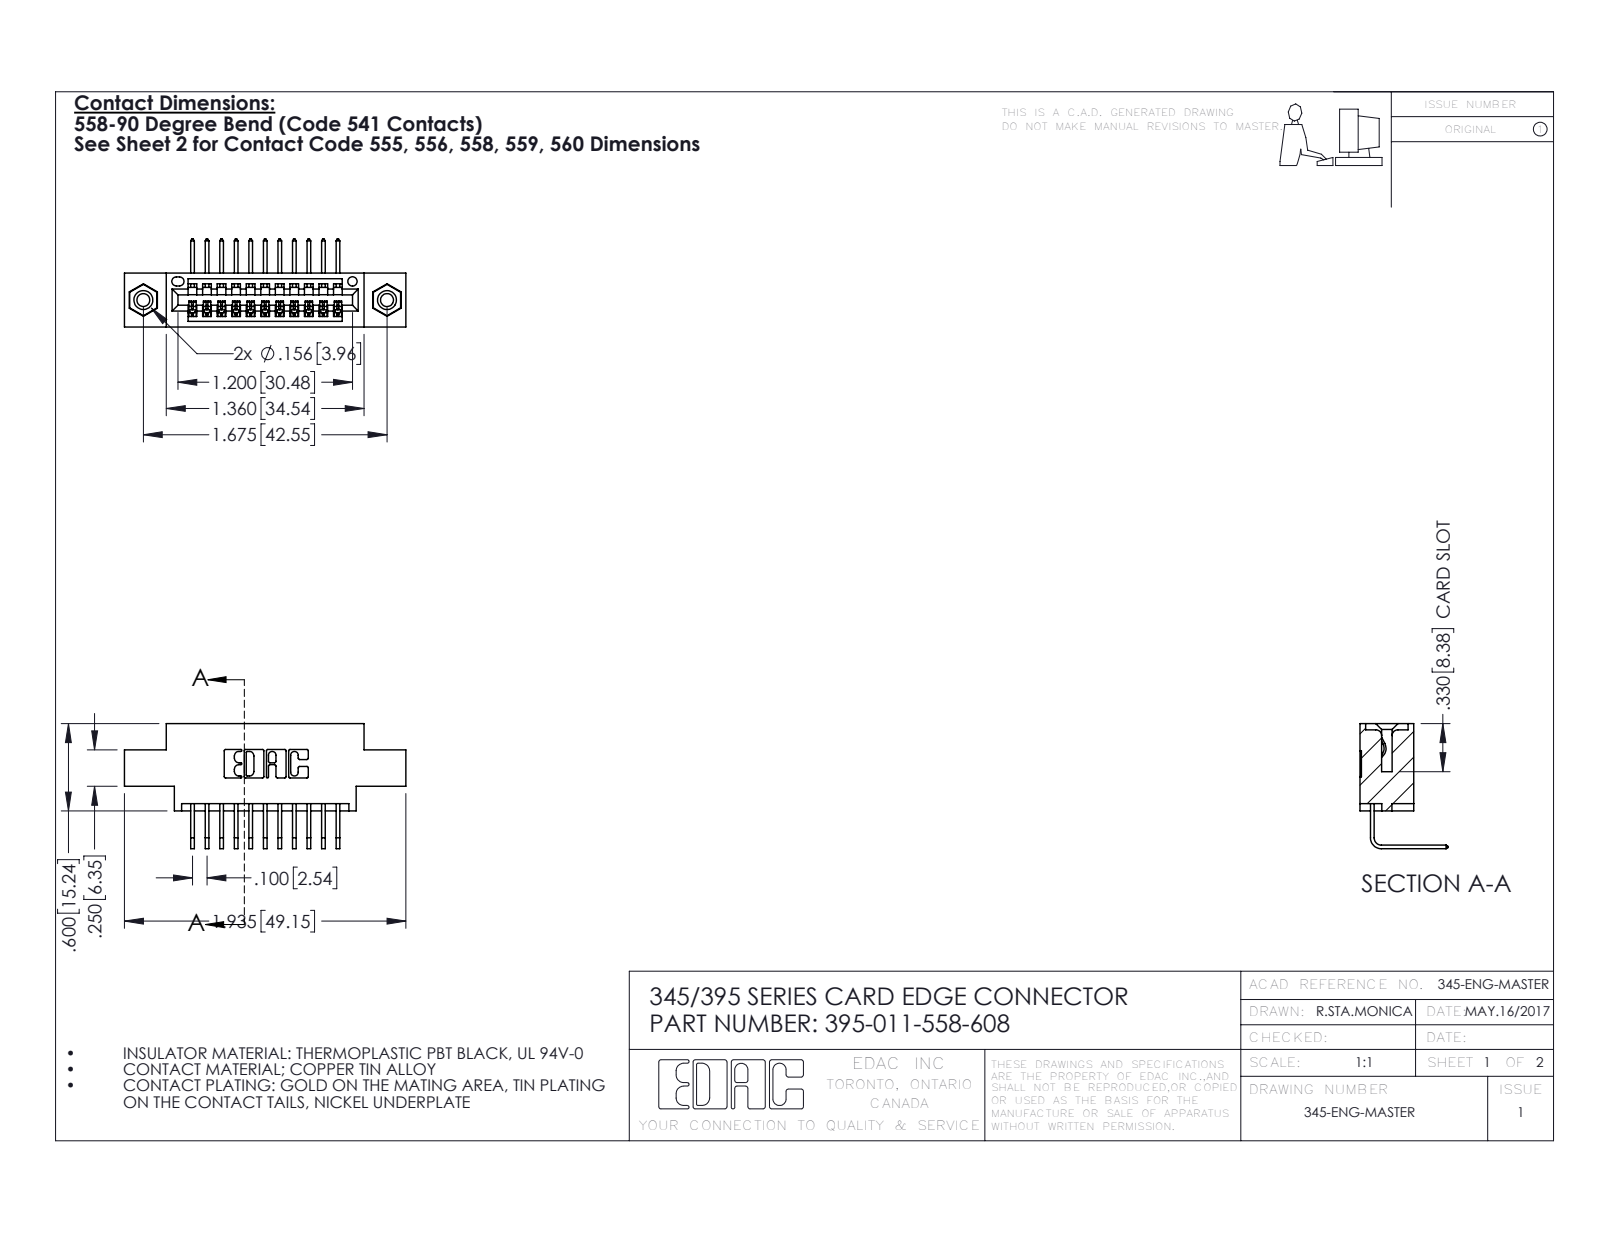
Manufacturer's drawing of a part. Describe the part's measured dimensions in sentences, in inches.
The part is named "345 Part_0.170 Offset - 0.156 Dia-TI; 345-292-001_558 Tail - 2; 395-011-558-608; 345-250-001_345-250-003-102". Its 3-D file was written by "SolidWorks 2016 (CONFIG_CONTROL_DESIGN)". It is 14 solids with 850 faces: 578 planar, 256 cylindrical and 16 other. Overall it measures 1.935 by 0.859 by 0.605 inches. Its volume is 0.264 cubic inches and its surface area 8.828 square inches. Round holes: 2 of diameter 0.089, 2 of diameter 0.125, 2 of diameter 0.156, 1 of diameter 0.064. Round bosses or shafts: 2 of diameter 0.155. Partial cylindrical surfaces (rounded edges, fillets, slot ends): 22 of radius 0.006, 22 of radius 0.01, 6 of radius 0.007, 6 of radius 0.031, 3 of radius 0.026, 2 of radius 0.031, 2 of radius 0.04, 1 of radius 0.014. The main face-to-face distances are 0.37, 0.072, 0.298, 0.2, 0.098, 0.272, 0.025, 0.1, 0.6, 0.225. The hole center spacings are 0.27, 1.443, 1.675.
